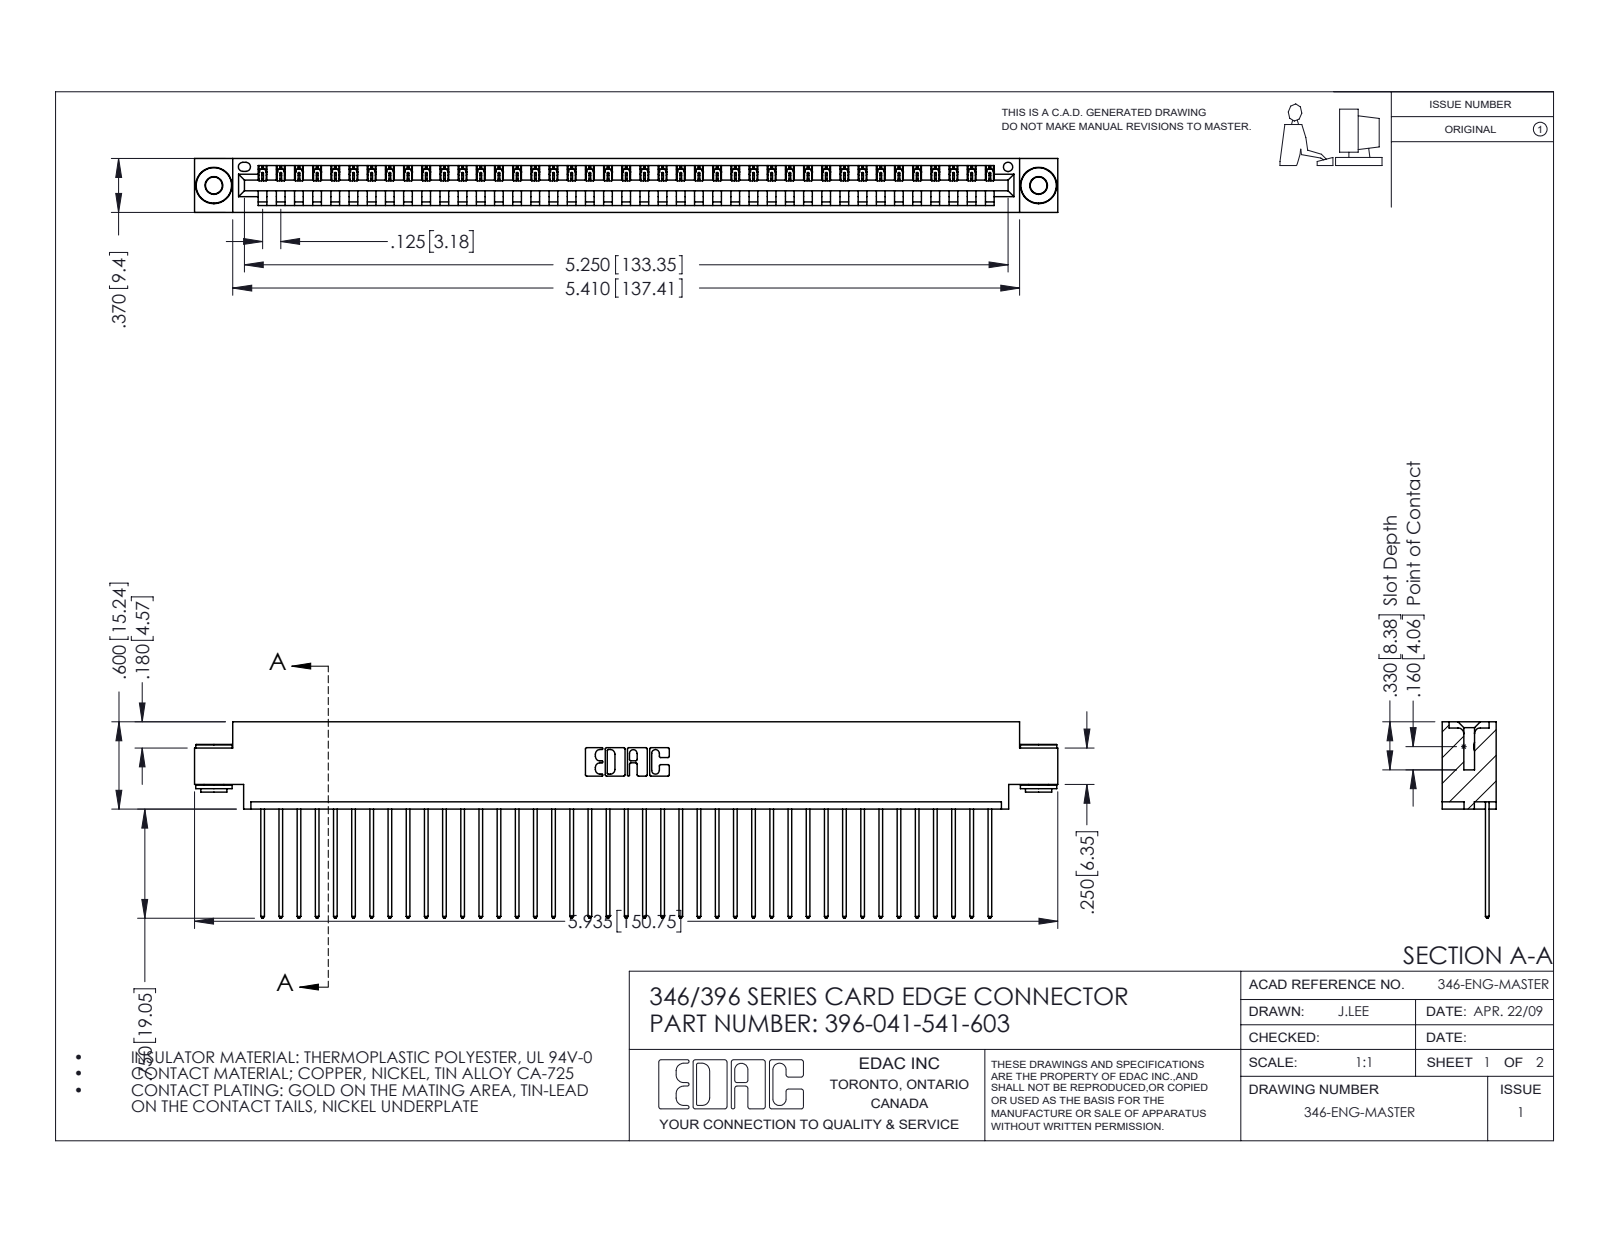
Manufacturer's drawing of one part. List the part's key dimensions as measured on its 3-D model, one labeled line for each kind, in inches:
Part name (STEP PRODUCT): 345-250-002_345-250-002-102; 346 Part_0.170 Offset - 0.156 Dia-TH; 345-292-001_345-293-141; 396-041-541-603
STEP written by: SolidWorks 2016 (CONFIG_CONTROL_DESIGN)
Units: inches
Bodies: 44 solids, 2542 faces (1730 planar, 804 cylindrical, 8 other)
Overall size (bounding box): 5.935 × 1.35 × 0.37
Volume: 0.88 in³ · Surface area: 29.77 in²
Round holes (diameter × count): ⌀0.116 ×2, ⌀0.156 ×2, ⌀0.064 ×1
Round bosses / shafts (diameter × count): ⌀0.25 ×2, ⌀0.18 ×2, ⌀0.136 ×2
Partial cylindrical surfaces — rounded edges, fillets, slot ends (radius × count): R0.006 ×82, R0.01 ×82, R0.01 ×22, R0.007 ×6, R0.031 ×6, R0.026 ×3, R0.031 ×2, R0.04 ×2
Main face-to-face distances: 0.048, 0.322, 0.37, 0.25, 0.025, 0.072, 0.298, 0.148, 0.222, 0.1
Hole centre spacings: 0.246, 5.461, 5.67
